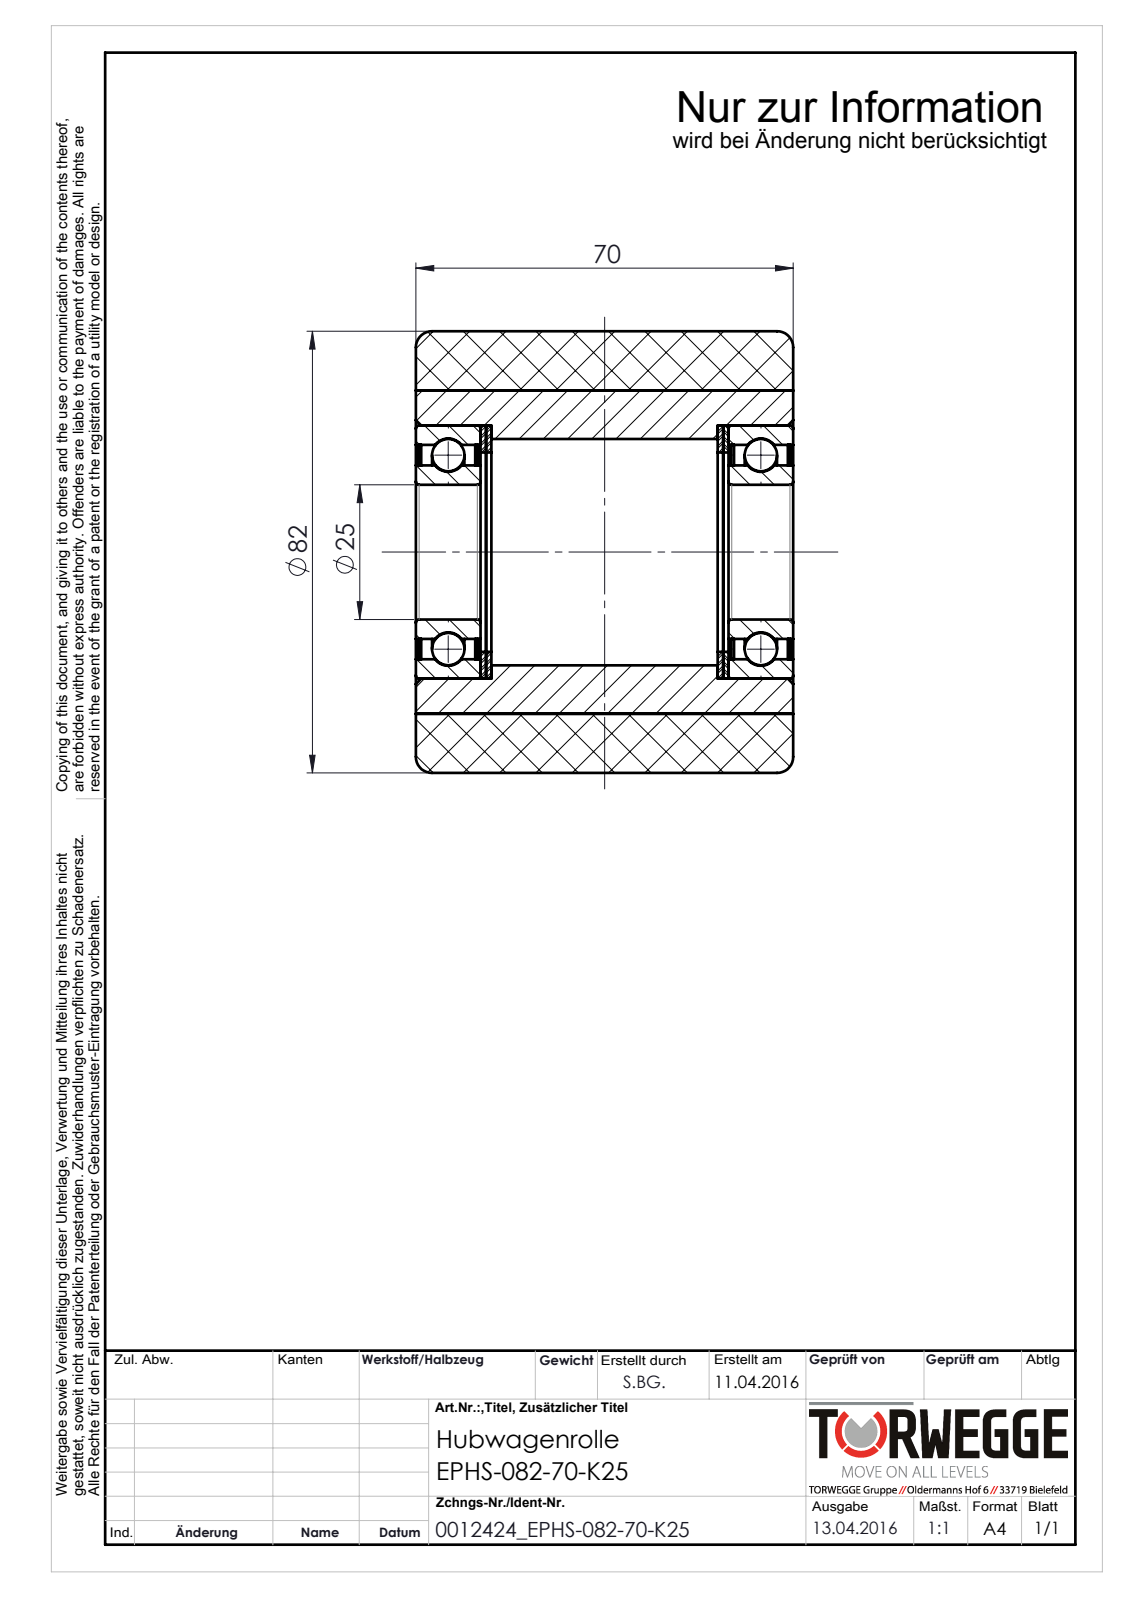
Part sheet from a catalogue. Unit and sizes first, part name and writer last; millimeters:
Units: millimetres
Overall size (bounding box): 82 × 82 × 70
Round holes (diameter × count): ⌀25 ×1, ⌀32.2 ×1, ⌀37 ×1, ⌀39.8 ×1, ⌀42 ×1, ⌀60 ×1
Round bosses / shafts (diameter × count): ⌀82 ×1, ⌀47 ×1
Main face-to-face distances: 1, 58, 12, 0.5, 13, 57, 45, 70, 44, 56
Volume: 289 264 mm³ · Surface area: 89 617 mm²
Bodies: 16 solids, 158 faces (30 planar, 68 cylindrical, 60 other)
Part name (STEP PRODUCT): 0012424_EPHS-082-70-K25
STEP written by: SolidWorks 2016 (AUTOMOTIVE_DESIGN)
